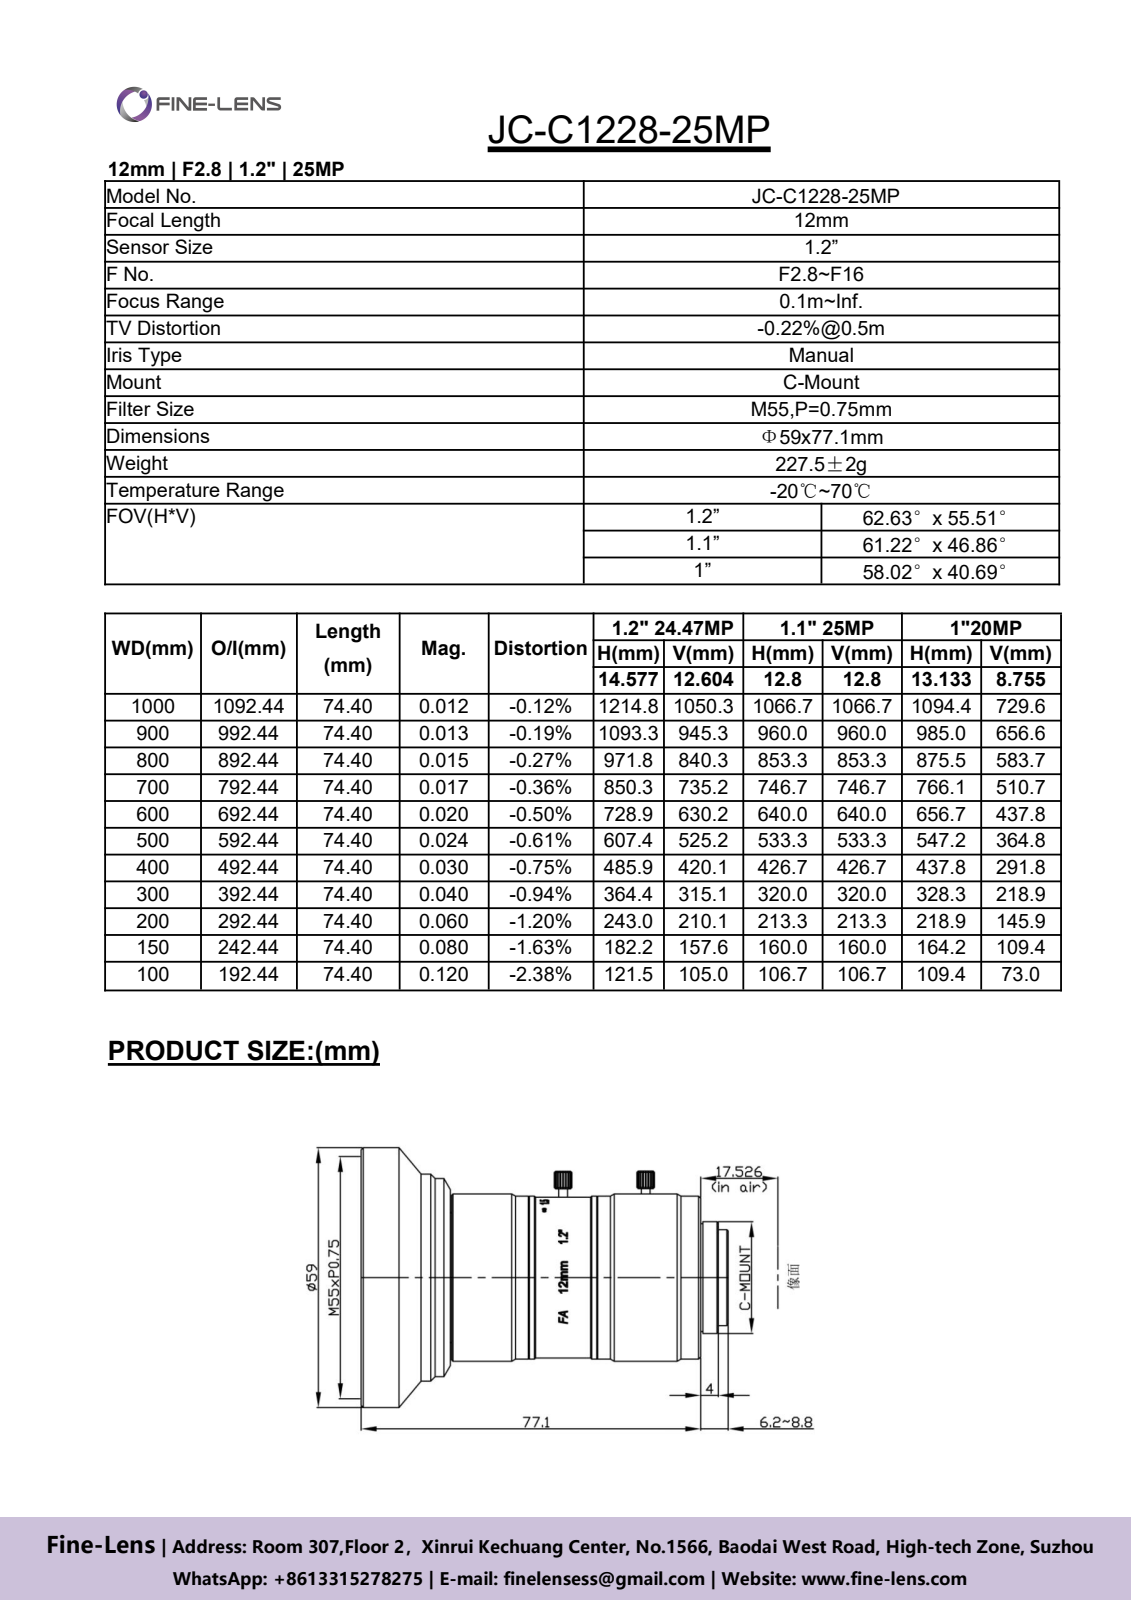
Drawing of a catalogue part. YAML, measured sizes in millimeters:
part_name: "LB-1; SNZFS-M1.6-3; F12mm; 锁紧钉1"
step_written_by: "SolidWorks 2022 (CONFIG_CONTROL_DESIGN)"
units: millimeters
bodies: {solids: 8, faces: 966, planar: 407, cylindrical: 222, other: 337}
overall_size: [83.33, 59, 59]
volume: 94249
surface_area: 25724
round_holes:
  - {diameter: 2, count: 4}
  - {diameter: 1.7, count: 3}
  - {diameter: 3, count: 1}
  - {diameter: 17.85, count: 1}
  - {diameter: 18.15, count: 1}
  - {diameter: 18.45, count: 1}
  - {diameter: 18.75, count: 1}
  - {diameter: 20.01, count: 1}
  - {diameter: 22, count: 1}
  - {diameter: 40.46, count: 1}
  - {diameter: 41.26, count: 1}
  - {diameter: 41.97, count: 1}
round_bosses_or_shafts:
  - {diameter: 2.3, count: 3}
  - {diameter: 1.6, count: 3}
  - {diameter: 59, count: 1}
  - {diameter: 47, count: 1}
  - {diameter: 46.2, count: 1}
  - {diameter: 45, count: 1}
  - {diameter: 41.45, count: 1}
  - {diameter: 38, count: 1}
partial_cylinders:
  - {radius: 2, count: 2}
  - {radius: 18.24, count: 1}
  - {radius: 18.49, count: 1}
face_to_face_distances: [7.12, 15.5, 8.38, 72.36, 65.24, 56.86, 0.36, 15.86, 8.74, 56.5]
hole_center_spacings: [15, 25.98, 17.45]
